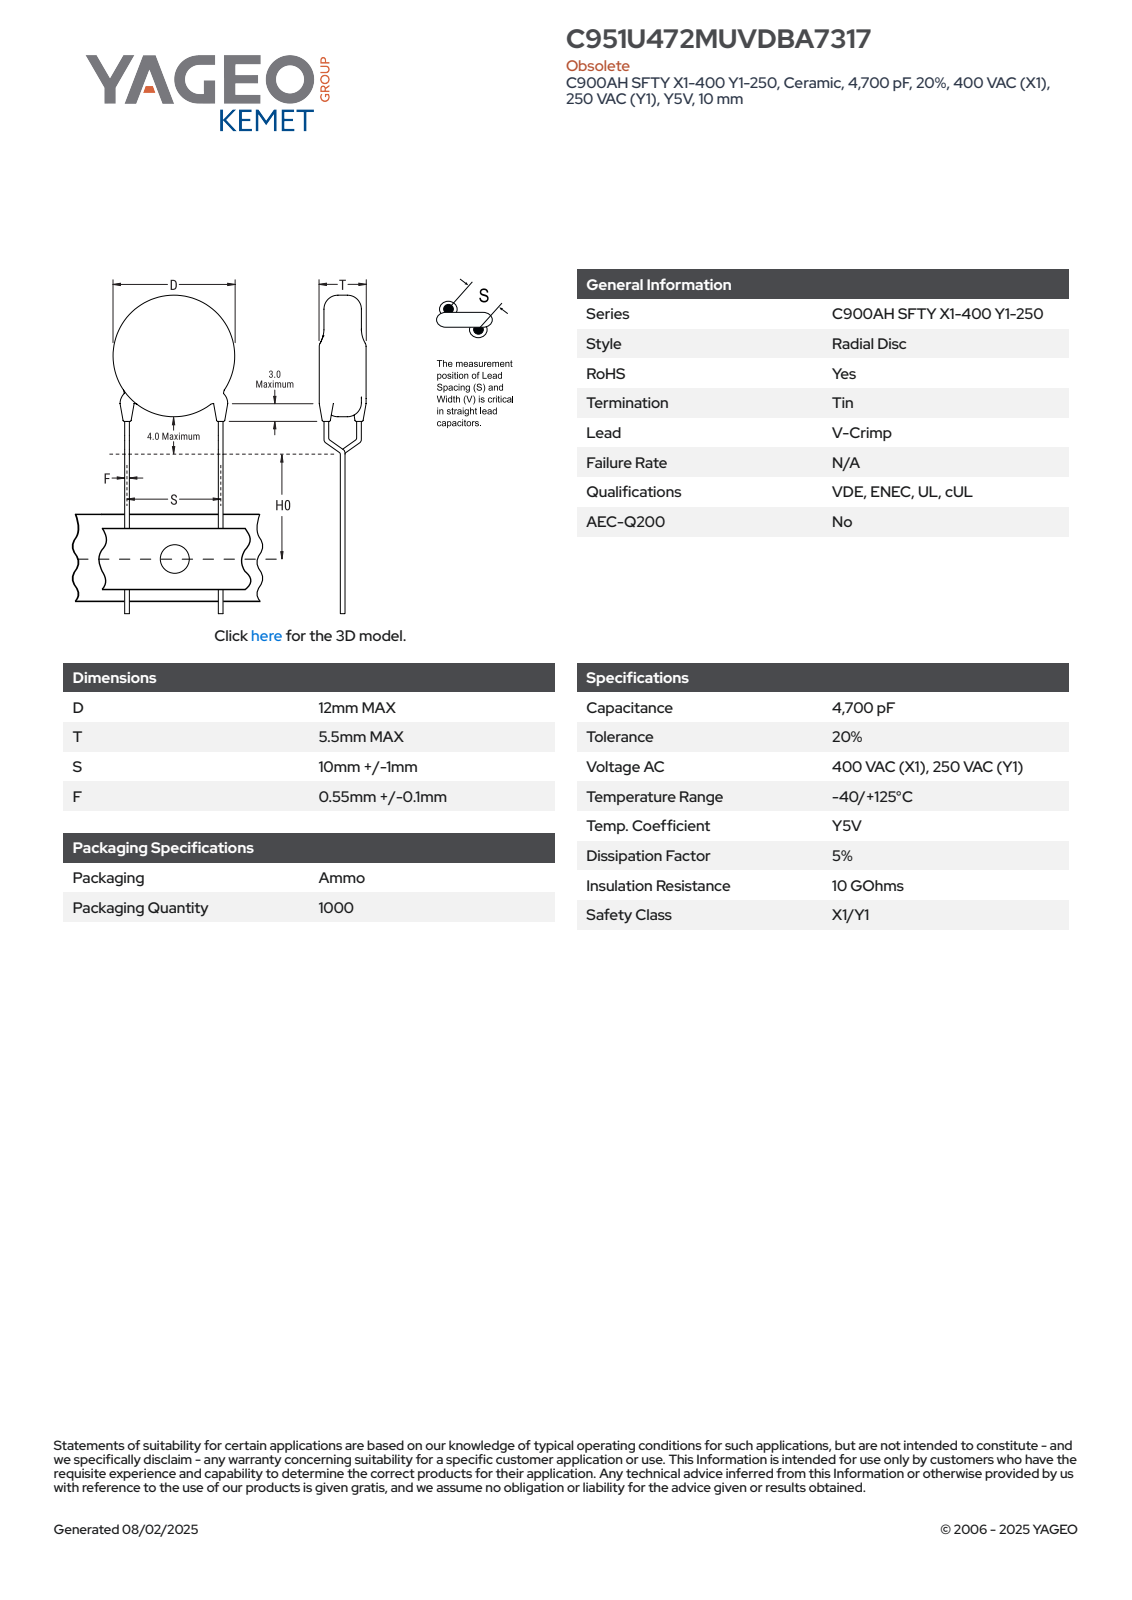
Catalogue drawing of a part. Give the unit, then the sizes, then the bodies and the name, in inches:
Units: inches
Overall size (bounding box): 1.409 × 0.472 × 0.217
Round bosses / shafts (diameter × count): ⌀0.026 ×6, ⌀0.472 ×1
Main face-to-face distances: 0.217, 0.902, 1.204, 0.302, 1.143, 0.241, 0.061, 0.017, 0.015, 0.05
Volume: 0.038 in³ · Surface area: 0.815 in²
Bodies: 5 solids, 93 faces (65 planar, 16 cylindrical, 12 other)
Part name (STEP PRODUCT): CCD_VCC900_D12T5.5S10LL20F0.65
STEP written by: SolidWorks 2014 (AUTOMOTIVE_DESIGN)
